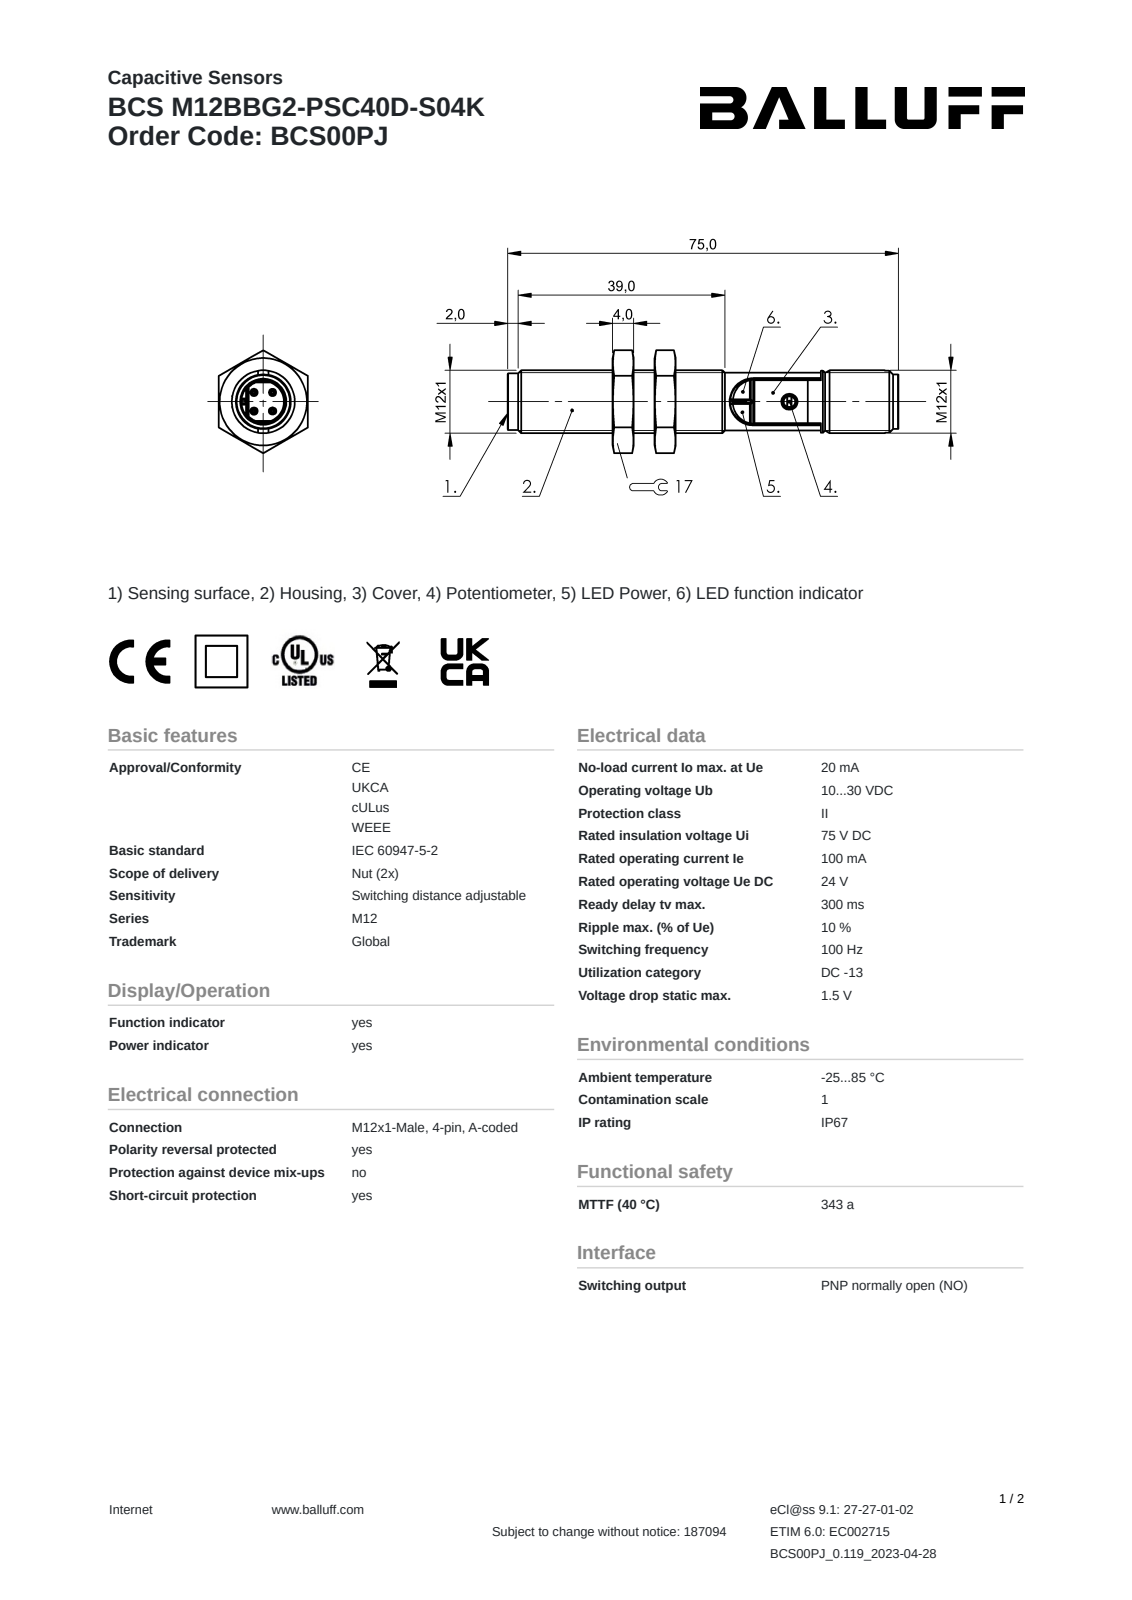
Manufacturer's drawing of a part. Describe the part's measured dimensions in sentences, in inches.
The part is named "BCS00PJ". Its 3-D file was written by "SolidWorks 2021 (AUTOMOTIVE_DESIGN)". It is 3 solids with 180 faces: 86 planar, 49 cylindrical and 45 other. Overall it measures 2.953 by 0.773 by 0.669 inches. Its volume is 0.526 cubic inches and its surface area 7.44 square inches. Round holes: 1 of diameter 0.135, 1 of diameter 0.331, 1 of diameter 0.43. Round bosses or shafts: 4 of diameter 0.039, 1 of diameter 0.472, 1 of diameter 0.467, 1 of diameter 0.423, 1 of diameter 0.407, 1 of diameter 0.406. Partial cylindrical surfaces (rounded edges, fillets, slot ends): 8 of radius 0.004, 2 of radius 0.006, 2 of radius 0.009, 1 of radius 0.01, 1 of radius 0.024, 1 of radius 0.061, 1 of radius 0.156, 1 of radius 0.157. The main face-to-face distances are 0.276, 0.157, 0.669, 0.433, 0.118, 1.043, 0.886, 0.768, 0.61, 1.563.
